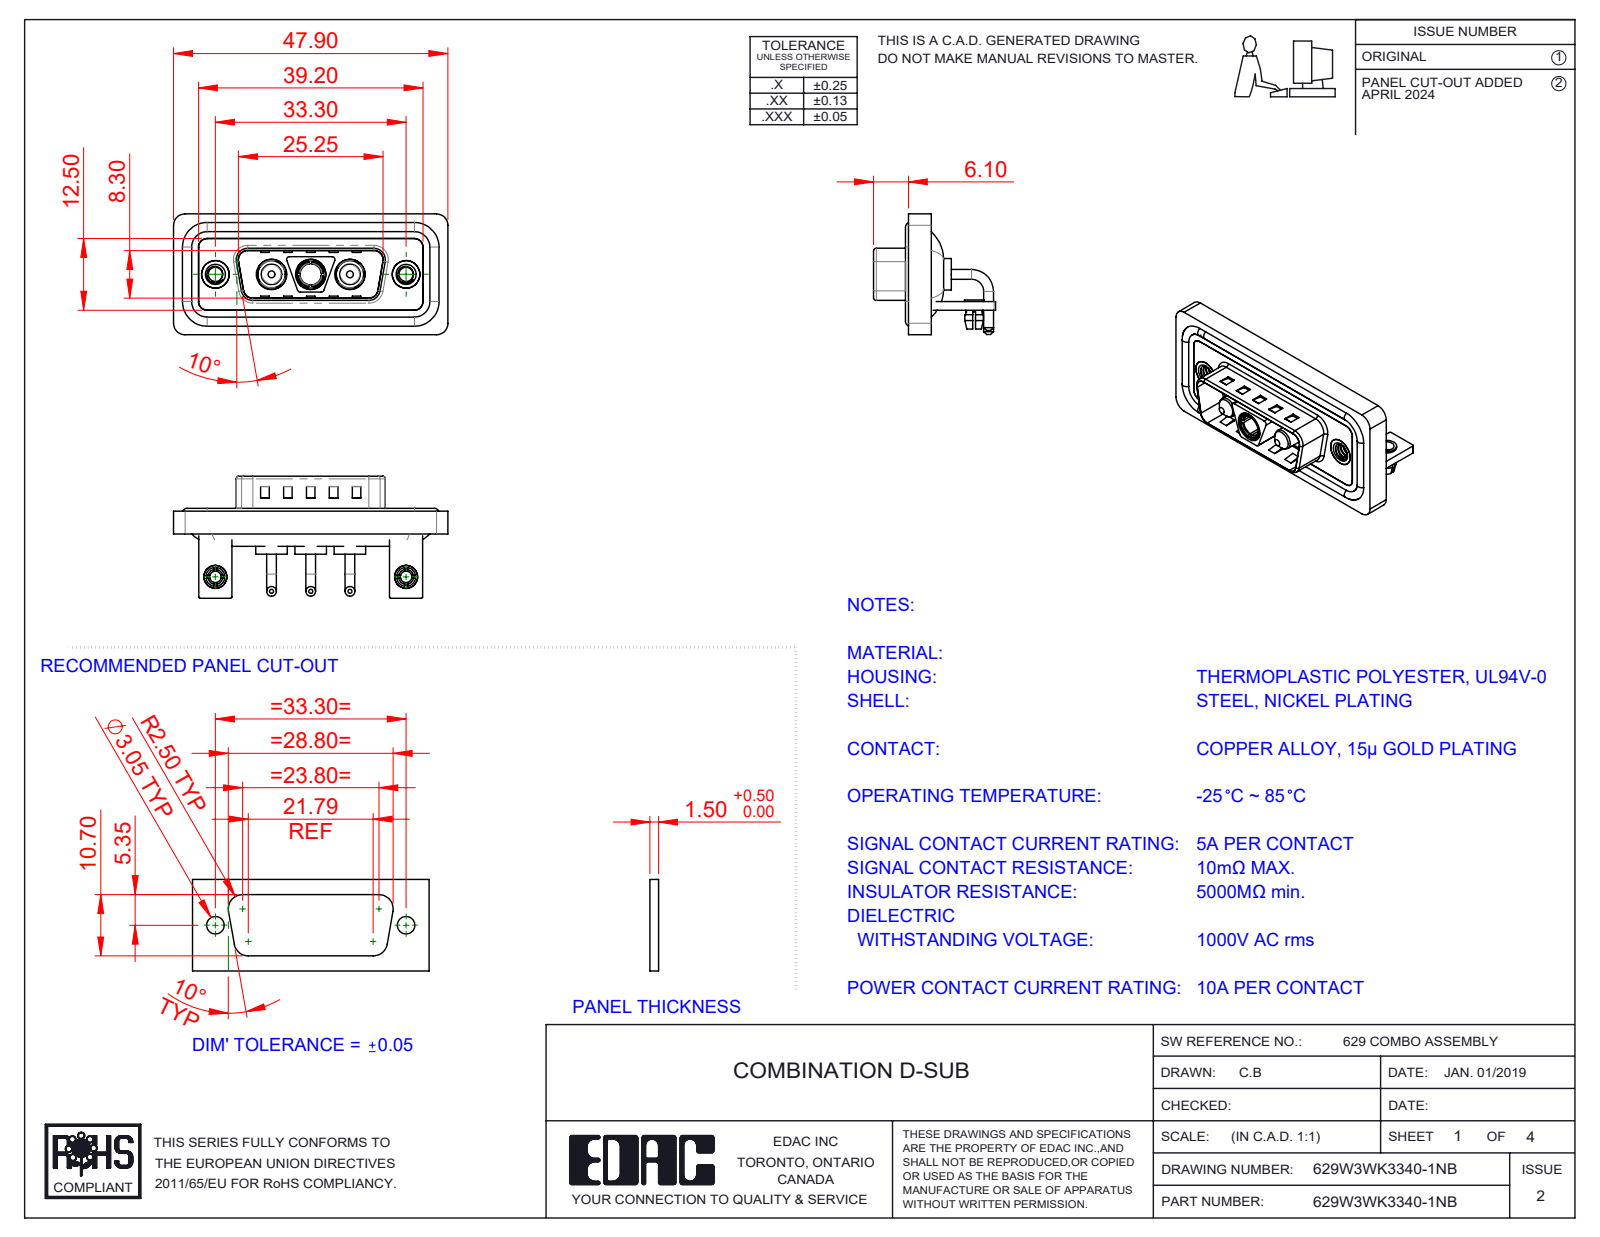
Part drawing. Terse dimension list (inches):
name: 629Combo Threaded Rivet_B; 629Combo Housing_3WK3; 629W3WK3340-1NB; 629Combo Board Lock (+6 more)
written by: SolidWorks 2023 (CONFIG_CONTROL_DESIGN)
unit: in
bodies: 17 solids, 751 faces (299 planar, 306 cylindrical, 146 other)
size: 1.886 × 0.839 × 0.831
volume: 0.367 in³; area: 15.59 in²
holes: 4× ⌀0.098, 3× ⌀0.191, 3× ⌀0.209, 2× ⌀0.079, 2× ⌀0.126, 2× ⌀0.157, 2× ⌀0.189, 2× ⌀0.197, 1× ⌀0.146
bosses: 6× ⌀0.067, 4× ⌀0.063, 3× ⌀0.217, 3× ⌀0.205, 3× ⌀0.187, 3× ⌀0.148, 2× ⌀0.193, 2× ⌀0.157
rounds: 21× R0.079, 18× R0.059, 16× R0.01, 13× R0.02, 8× R0.063, 4× R0.024, 4× R0.026, 4× R0.035
face distances: 0.016, 0.059, 0.031, 0.114, 0.043, 0.083, 0.146, 0.063, 0.047, 0.177
hole spacings: 0.27, 0.386, 0.656, 0.925, 1.311, 0.539
